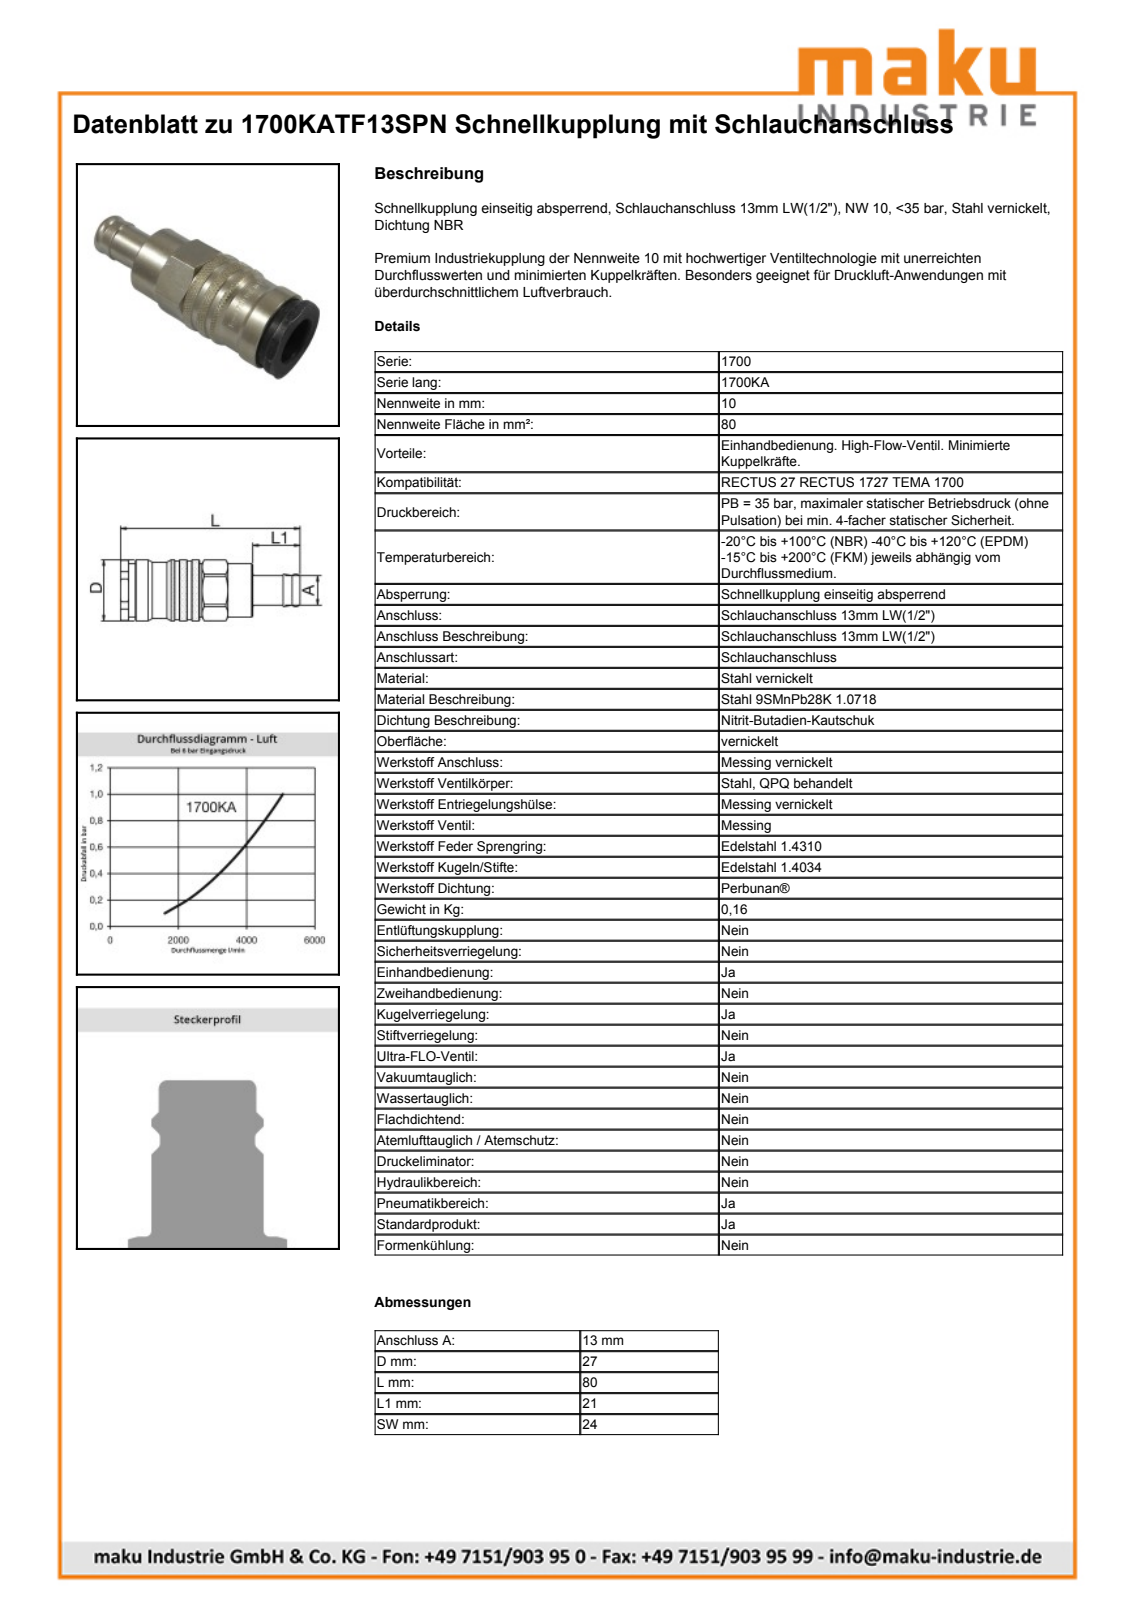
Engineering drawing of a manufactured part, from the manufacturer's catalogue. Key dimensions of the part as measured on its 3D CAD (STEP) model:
Part name (STEP PRODUCT): D103705
STEP written by: Autodesk Inventor 2011 (AUTOMOTIVE_DESIGN)
Units: millimetres
Bodies: 2 solids, 666 faces (197 planar, 94 cylindrical, 375 other)
Overall size (bounding box): 79.64 × 27.05 × 26.8
Volume: 30 994 mm³ · Surface area: 12 482 mm²
Round holes (diameter × count): ⌀20.15 ×1, ⌀21.2 ×1, ⌀21.4 ×1, ⌀22.5 ×1, ⌀23.8 ×1, ⌀24 ×1
Round bosses / shafts (diameter × count): ⌀26.8 ×1, ⌀26 ×1, ⌀25 ×1, ⌀23.7 ×1, ⌀21.3 ×1, ⌀21 ×1, ⌀20.97 ×1, ⌀19.5 ×1
Partial cylindrical surfaces — rounded edges, fillets, slot ends (radius × count): R12.4 ×1, R13.5 ×1, R13.53 ×1
Main face-to-face distances: 24, 58.64, 1, 25, 79.64, 21, 30.64, 28, 49, 6.55
